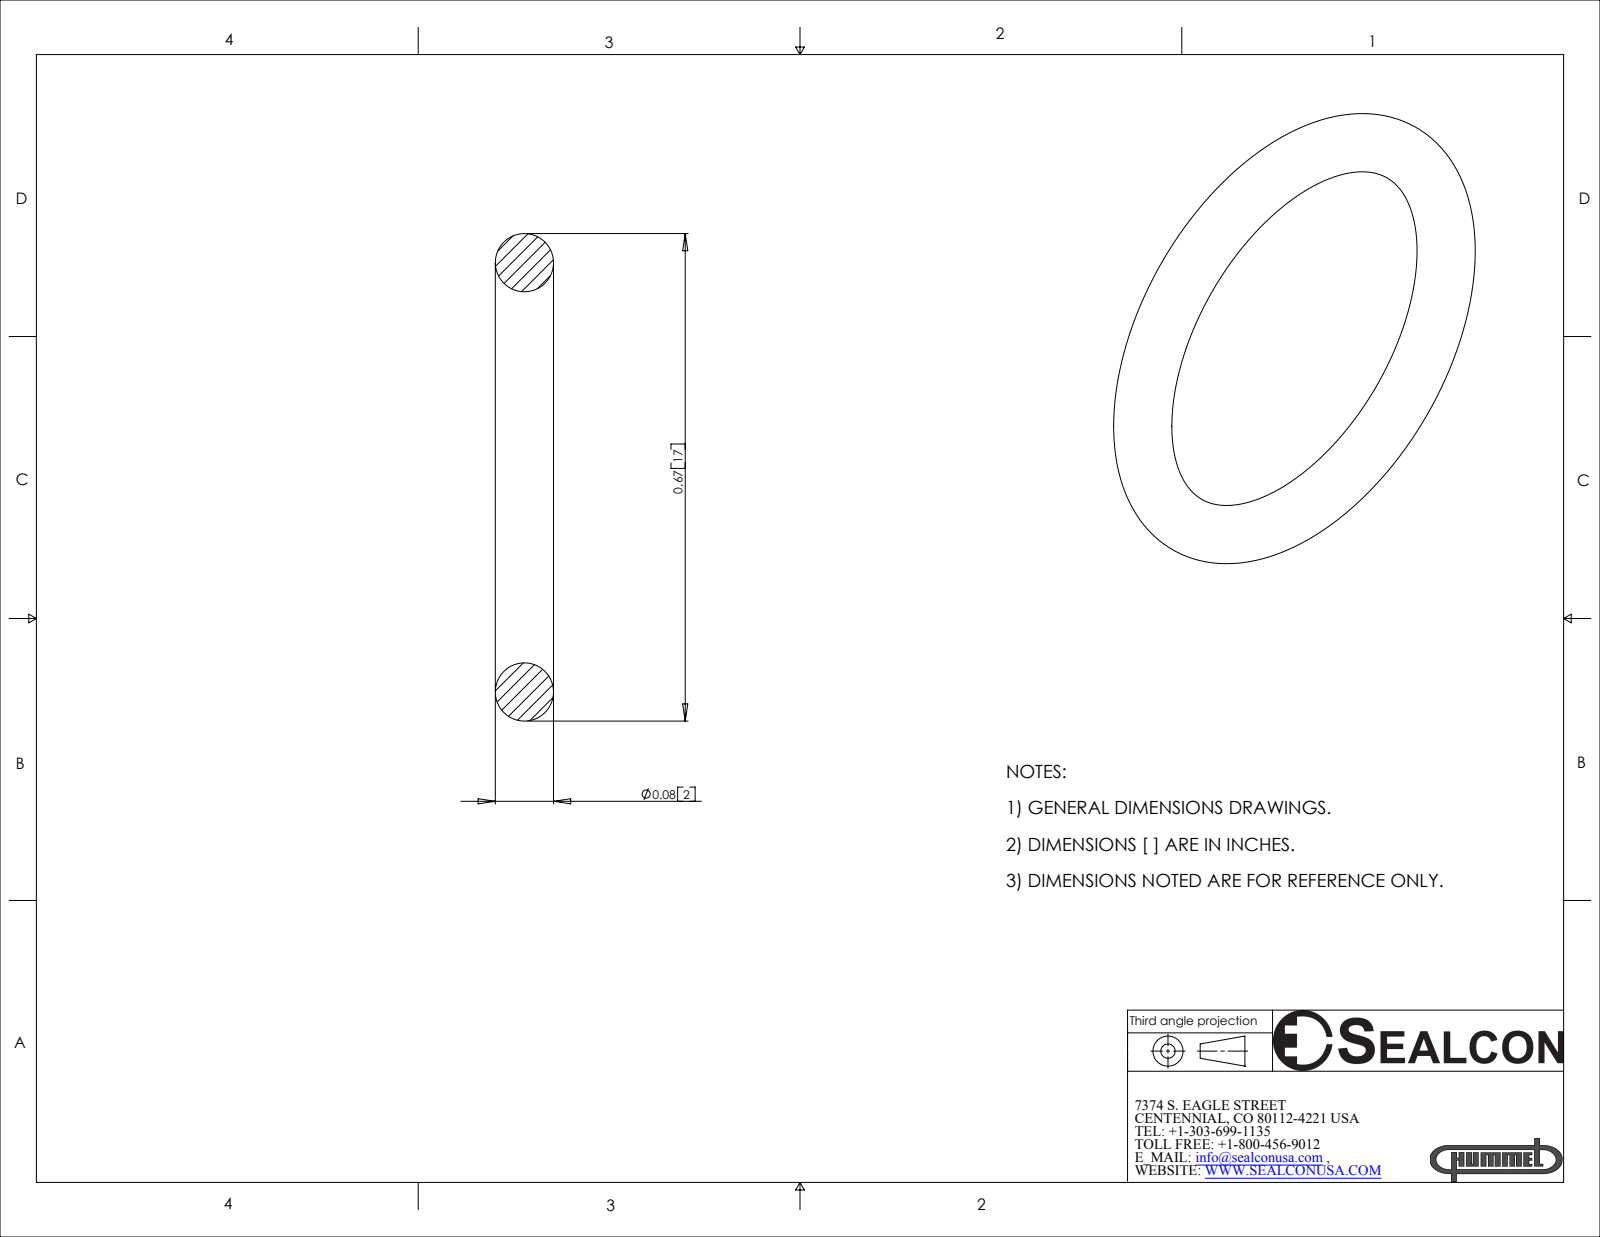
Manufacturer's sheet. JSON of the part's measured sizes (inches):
{"part_name": "OR-38-VT", "step_written_by": "SolidWorks 2007 (CONFIG_CONTROL_DESIGN)", "units": "inches", "bodies": {"solids": 1, "faces": 4, "planar": 0, "cylindrical": 0, "other": 4}, "overall_size": [0.67, 0.67, 0.08], "volume_in3": 0.009, "surface_area_in2": 0.466}
